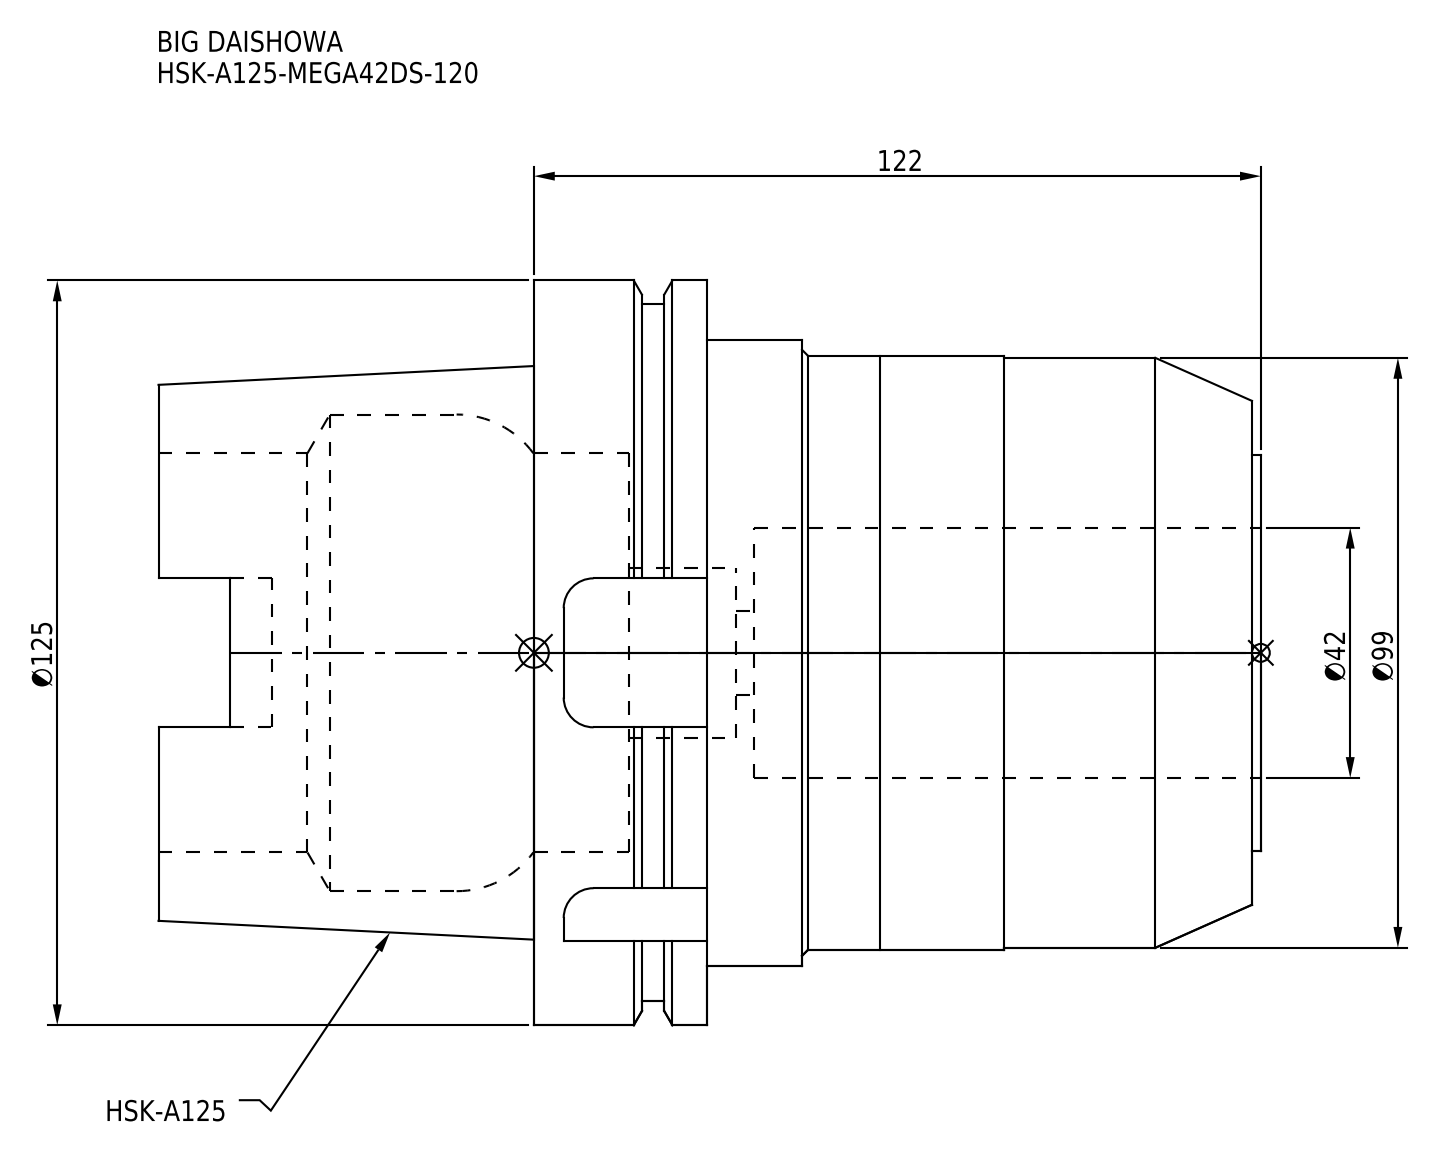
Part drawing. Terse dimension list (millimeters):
name: HSK-A125-MEGA42DS-120
written by: CREO PARAMETRIC BY PTC INC, 2016380 (AUTOMOTIVE_DESIGN)
unit: mm
bodies: 1 solid, 93 faces (38 planar, 39 cylindrical, 16 other)
size: 185 × 125 × 125
volume: 1 015 000 mm³; area: 113 549 mm²
holes: 1× ⌀14, 1× ⌀28.5, 1× ⌀42, 1× ⌀67, 1× ⌀80
bosses: 1× ⌀125, 1× ⌀117, 1× ⌀105, 1× ⌀99.7, 1× ⌀99, 1× ⌀66.5
rounds: 5× R5, 4× R5.88
face distances: 29, 13.05, 15.95, 1.5, 92, 78.95, 63, 91.5, 104.55, 120.5
